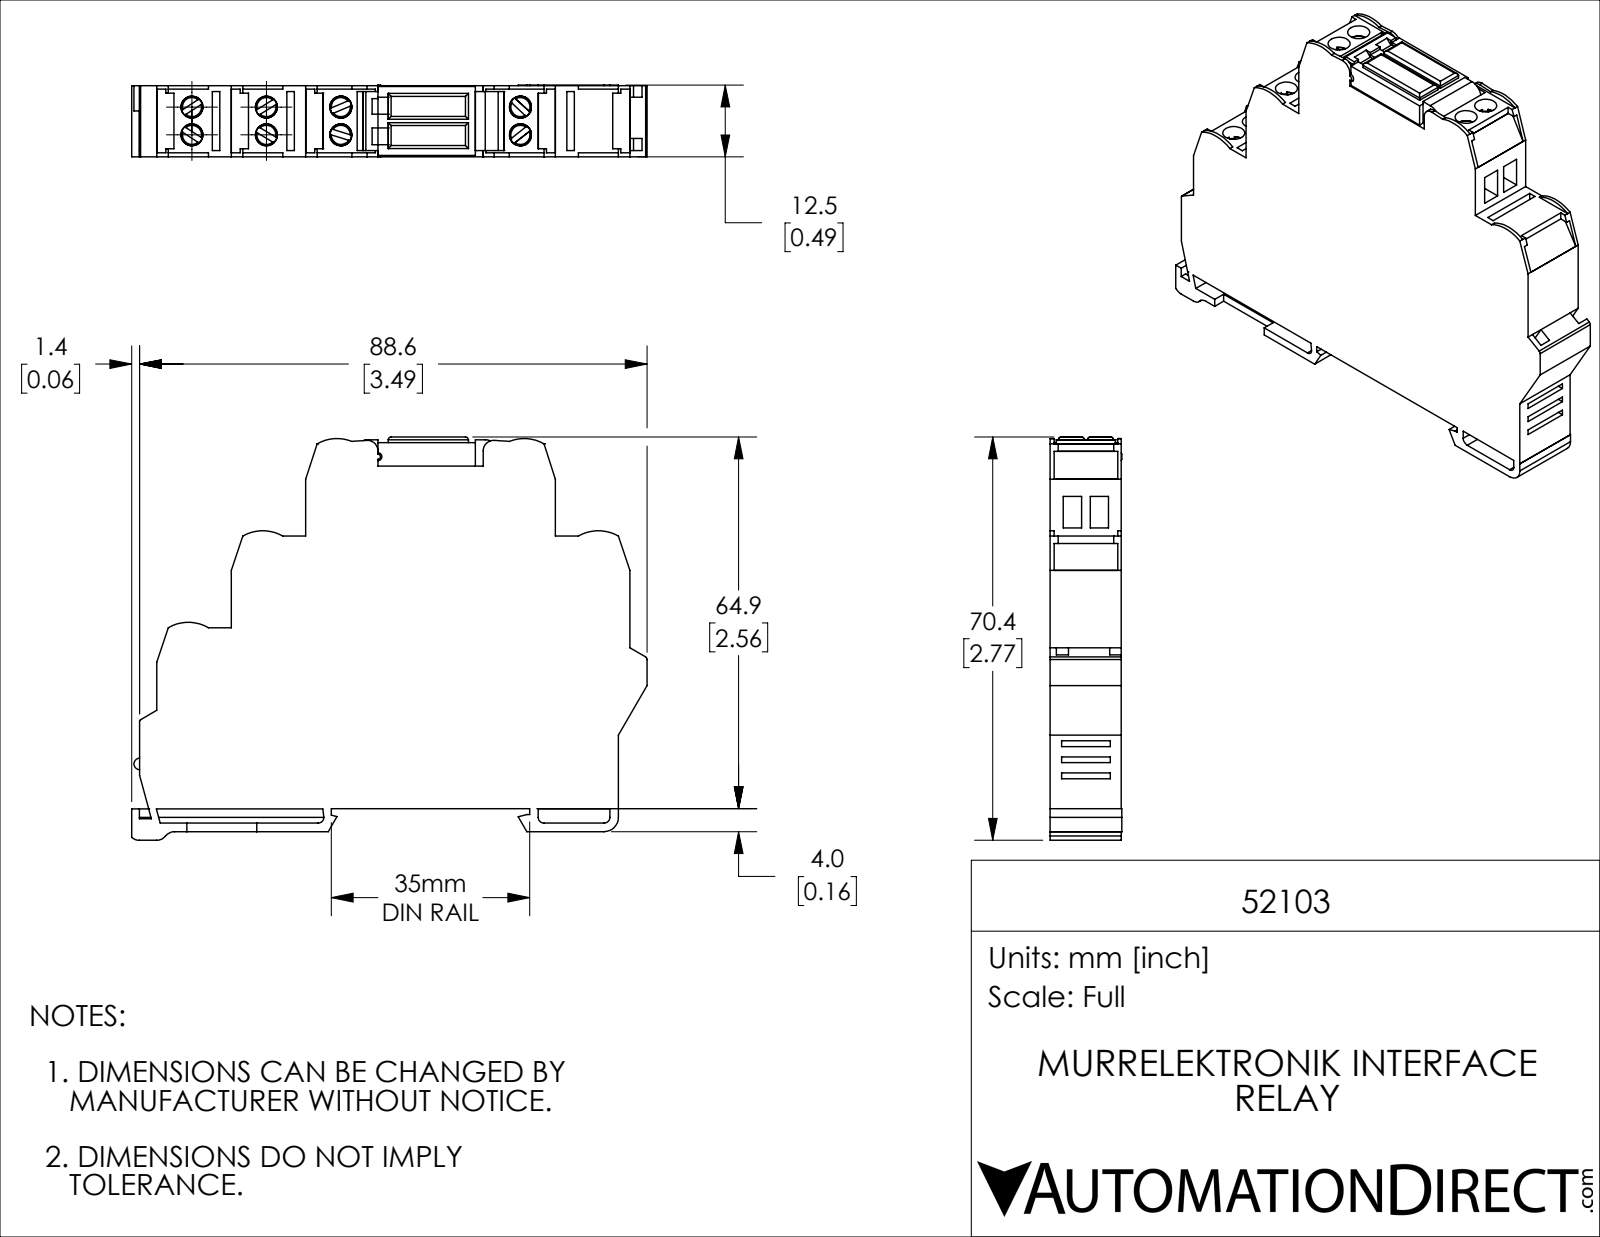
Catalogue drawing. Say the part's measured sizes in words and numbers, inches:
The part is named "52103". Its 3-D file was written by "SolidWorks 2019 (CONFIG_CONTROL_DESIGN)". It is 1 solid with 419 faces: 315 planar, 78 cylindrical and 26 other. Overall it measures 3.543 by 2.772 by 0.492 inches. Its volume is 3.294 cubic inches and its surface area 27.11 square inches. Round holes: 8 of diameter 0.152. Round bosses or shafts: 8 of diameter 0.148. Partial cylindrical surfaces (rounded edges, fillets, slot ends): 9 of radius 0.02, 5 of radius 0.276, 4 of radius 0.039, 3 of radius 0.079, 2 of radius 0.028, 2 of radius 0.071, 2 of radius 0.089, 1 of radius 0.012. The main face-to-face distances are 0.488, 0.059, 0.157, 0.039, 0.098, 0.217, 0.185, 0.126, 0.207, 1.874. The hole center spacings are 0.512, 0.191, 0.546, 1.024, 1.041, 1.235, 1.249, 1.746.
